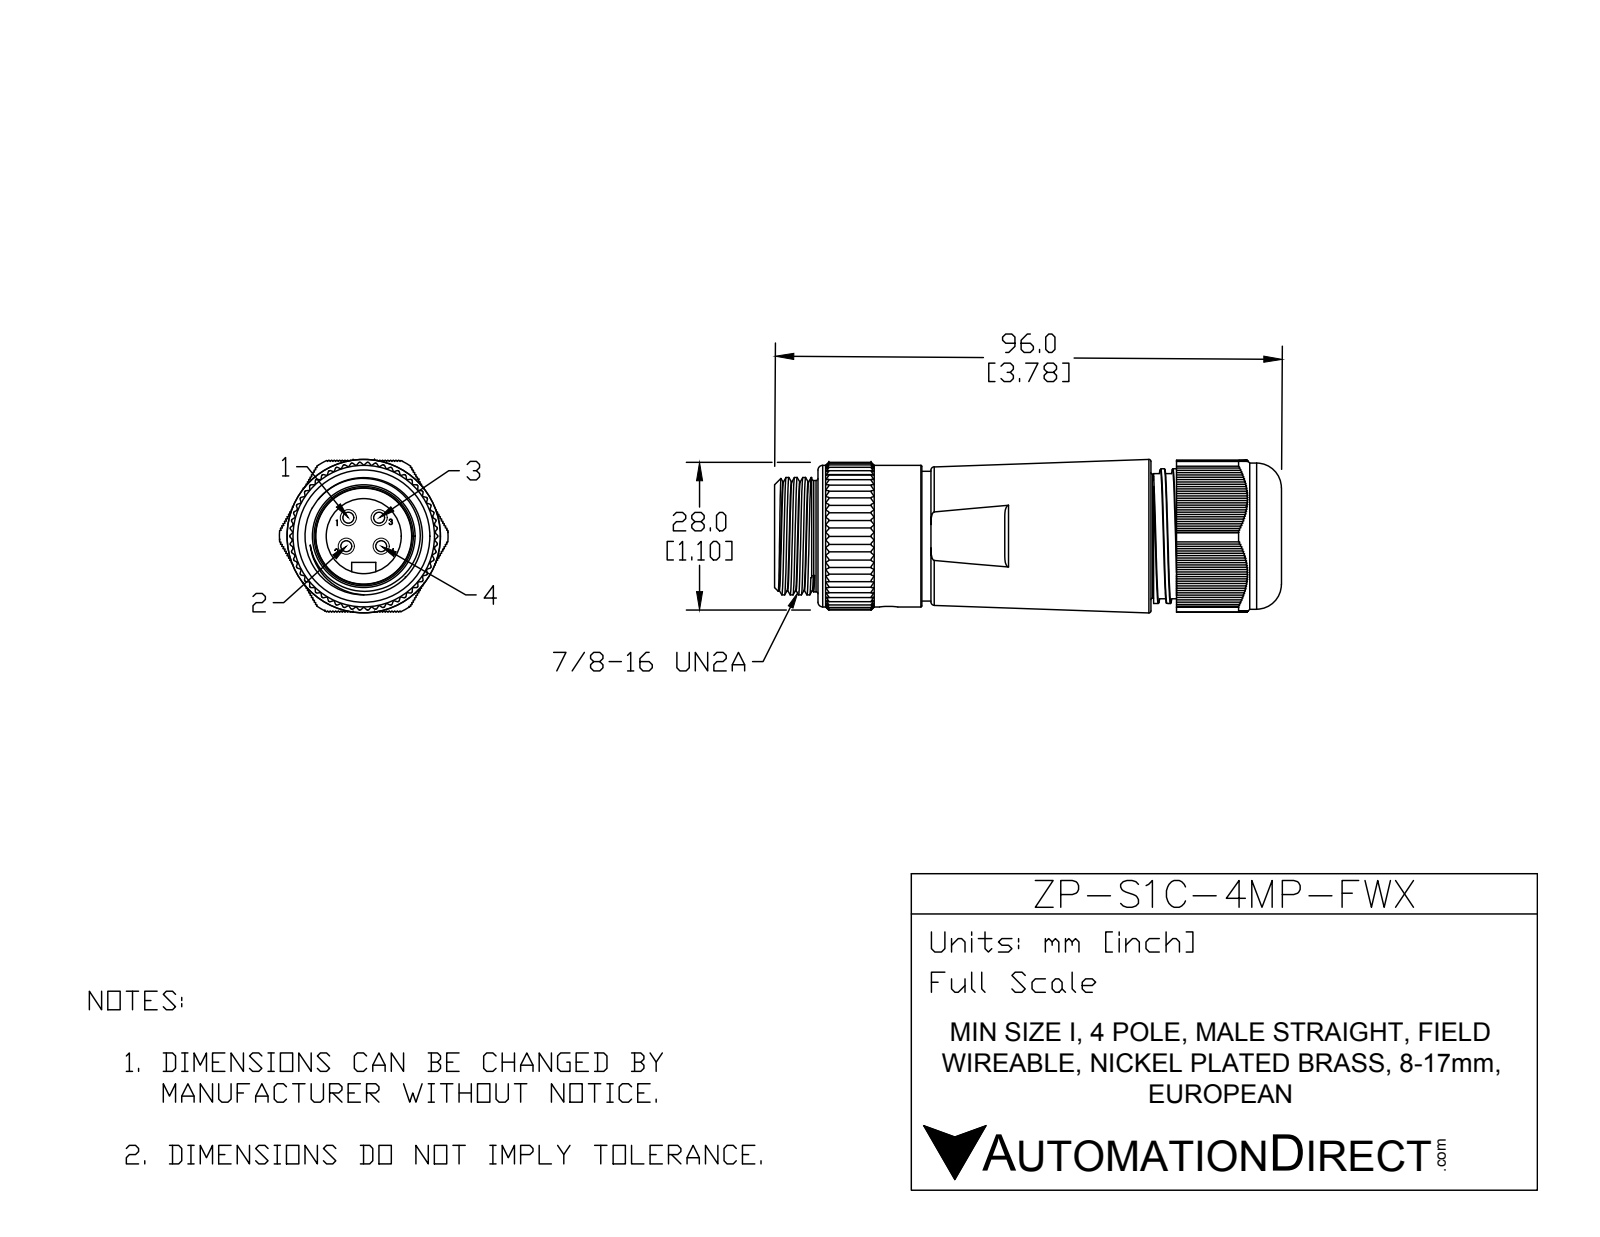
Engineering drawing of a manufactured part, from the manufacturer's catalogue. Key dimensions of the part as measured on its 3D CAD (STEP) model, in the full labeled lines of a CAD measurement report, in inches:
Part name (STEP PRODUCT): ZP-S1C-4MP-FWX
STEP written by: SolidWorks 2015 (AUTOMOTIVE_DESIGN)
Units: inches
Bodies: 8 solids, 910 faces (514 planar, 321 cylindrical, 75 other)
Overall size (bounding box): 3.791 × 1.256 × 1.144
Volume: 2.974 in³ · Surface area: 27.57 in²
Round holes (diameter × count): ⌀0.14 ×1, ⌀0.56 ×1, ⌀0.68 ×1, ⌀0.72 ×1, ⌀0.849 ×1, ⌀0.953 ×1, ⌀1 ×1
Round bosses / shafts (diameter × count): ⌀0.124 ×4, ⌀0.079 ×4, ⌀1.09 ×1, ⌀1.055 ×1, ⌀1.004 ×1, ⌀0.957 ×1, ⌀0.875 ×1, ⌀0.714 ×1
Partial cylindrical surfaces — rounded edges, fillets, slot ends (radius × count): R0.01 ×165, R0.09 ×1, R0.551 ×1, R0.628 ×1
Main face-to-face distances: 2.652, 0.042, 0.014, 0.028, 0.056, 0.083, 0.07, 0.346, 2.306, 0.014
